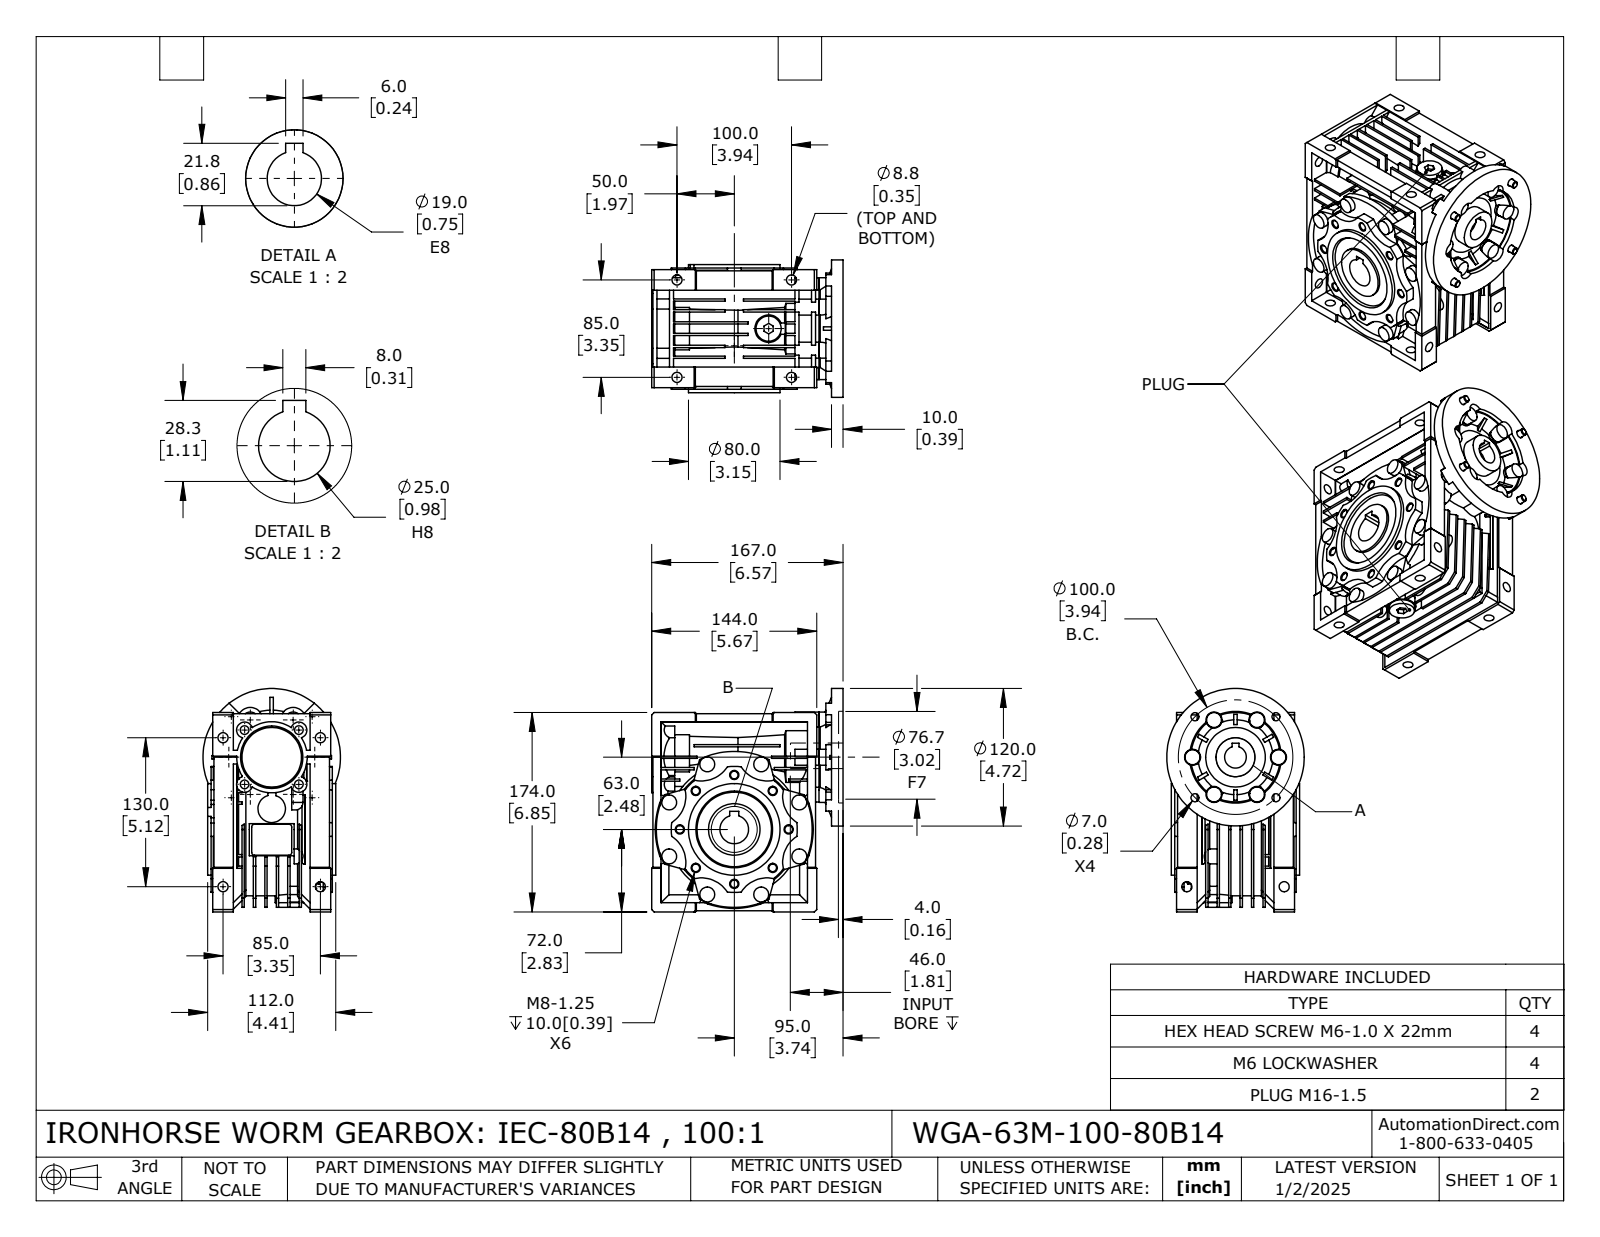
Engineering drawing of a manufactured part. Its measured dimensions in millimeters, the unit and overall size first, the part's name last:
Units: millimetres
Overall size (bounding box): 195 × 172.5 × 120
Round holes (diameter × count): ⌀6.65 ×8, ⌀8.78 ×8, ⌀6.1 ×4, ⌀7 ×4, ⌀7.56 ×4, ⌀14.5 ×2, ⌀19 ×1, ⌀20 ×1, ⌀25 ×1, ⌀34 ×1, ⌀37 ×1, ⌀45 ×1
Round bosses / shafts (diameter × count): ⌀13 ×14, ⌀14 ×6, ⌀12.2 ×4, ⌀6 ×4, ⌀24 ×3, ⌀22 ×2, ⌀15.8 ×2, ⌀13.7 ×2
Partial cylindrical surfaces — rounded edges, fillets, slot ends (radius × count): R7 ×10, R27 ×8, R6.98 ×6, R11 ×6, R2.5 ×4, R8.35 ×1, R29.5 ×1, R30.5 ×1
Main face-to-face distances: 10, 8, 20, 2, 30, 18, 12, 7, 40, 1
Hole centre spacings: 36.36, 47.5, 60.19, 67.18, 87.77, 16.5, 33.5, 47.38
Volume: 1 847 000 mm³ · Surface area: 350 234 mm²
Bodies: 16 solids, 1442 faces (853 planar, 413 cylindrical, 176 other)
Part name (STEP PRODUCT): WGA-63M-100-80B14
STEP written by: SolidWorks 2024 (CONFIG_CONTROL_DESIGN)
